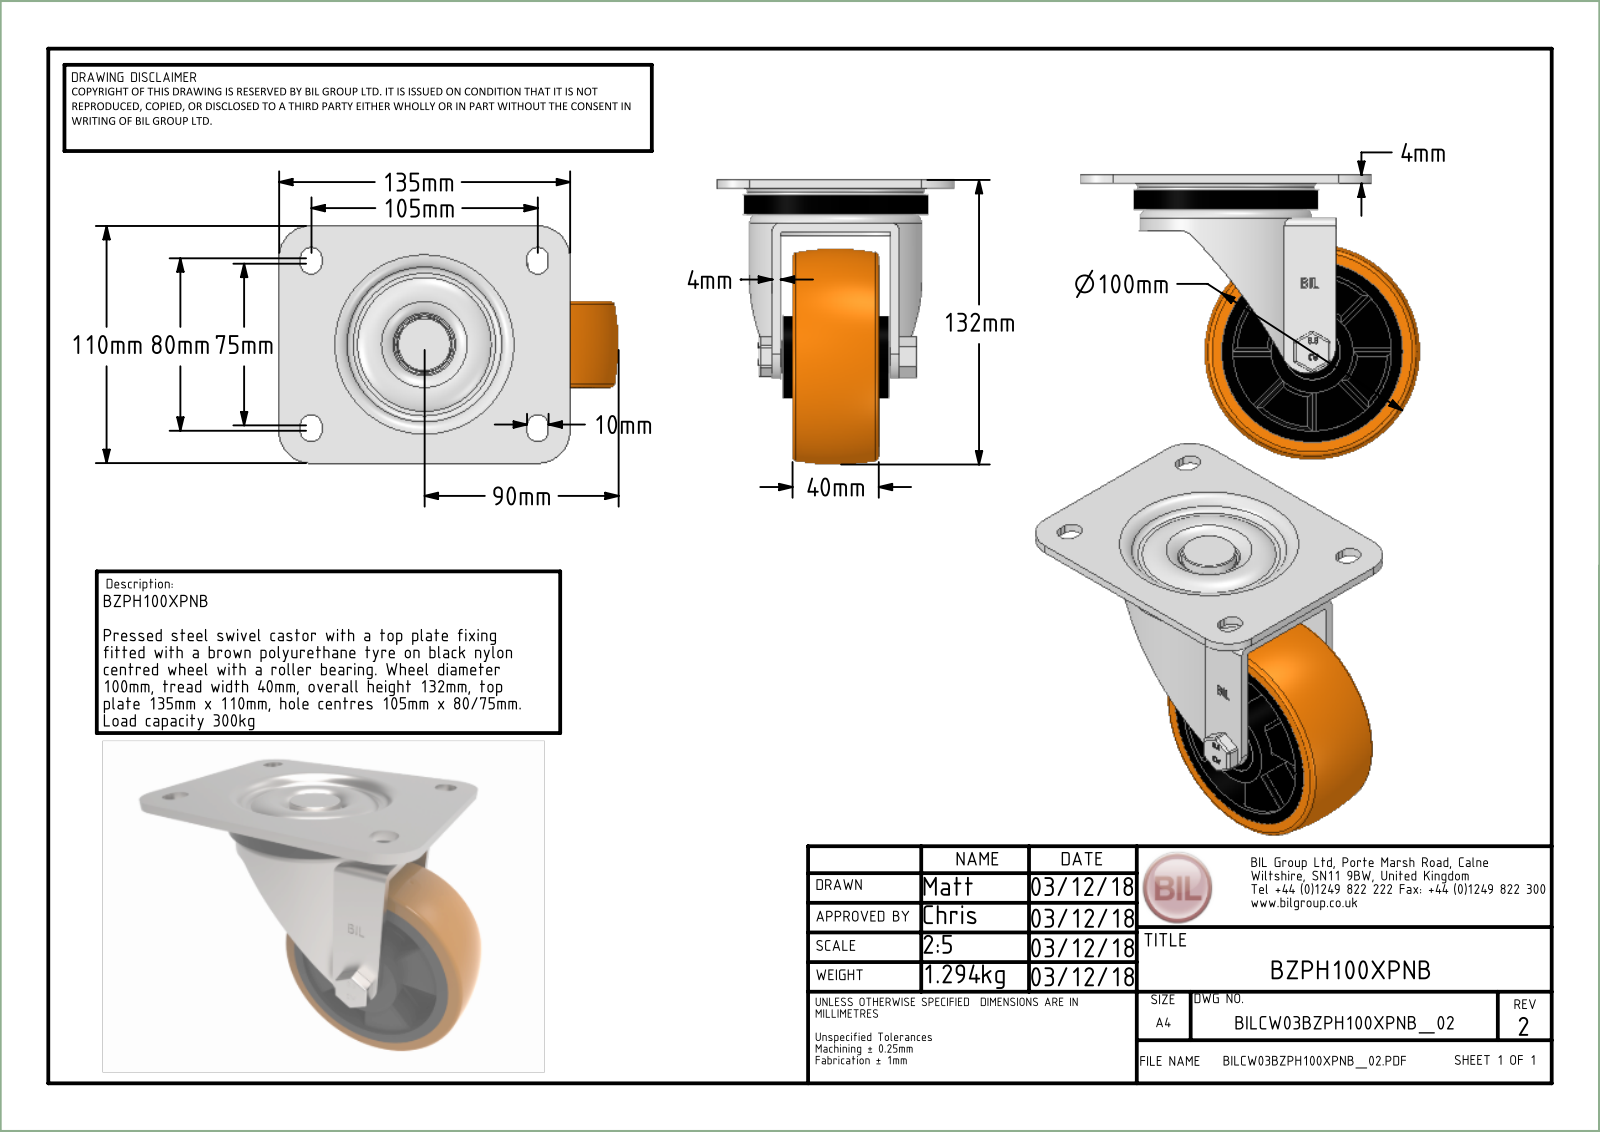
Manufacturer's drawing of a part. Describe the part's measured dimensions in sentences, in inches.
The part is named "BZPH100XPNB v3; BZPH100AS v1; ZINC PLATED, PRESSED STEEL TOP PLATE; ZINC PLATED, PRESSED STEEL FORKS (+8 more)". Its 3-D file was written by "Autodesk Translation Framework v14.10.0.0 (AUTOMOTIVE_DESIGN)". It is 20 solids with 678 faces: 267 planar, 149 cylindrical and 262 other. Overall it measures 6.201 by 5.197 by 4.331 inches. Its volume is 22.8 cubic inches and its surface area 250.7 square inches. Round holes: 2 of diameter 1.024, 1 of diameter 0.394, 1 of diameter 0.402, 1 of diameter 0.413, 1 of diameter 0.472, 1 of diameter 0.591, 1 of diameter 0.61, 1 of diameter 1.063, 1 of diameter 1.102, 1 of diameter 2.835, 1 of diameter 2.874, 1 of diameter 3.248. Round bosses or shafts: 8 of diameter 0.157, 1 of diameter 3.287, 1 of diameter 3.15, 1 of diameter 2.008, 1 of diameter 1.457, 1 of diameter 1.26, 1 of diameter 1.059, 1 of diameter 0.984. Partial cylindrical surfaces (rounded edges, fillets, slot ends): 18 of radius 0.02, 8 of radius 0.217, 6 of radius 0.03, 4 of radius 0.079, 4 of radius 0.591, 2 of radius 0.157, 1 of radius 0.364, 1 of radius 0.535. The main face-to-face distances are 0.157, 0.354, 0.512, 0.197, 0.374, 0.217, 1.752, 1.949, 1.575, 0.039.
